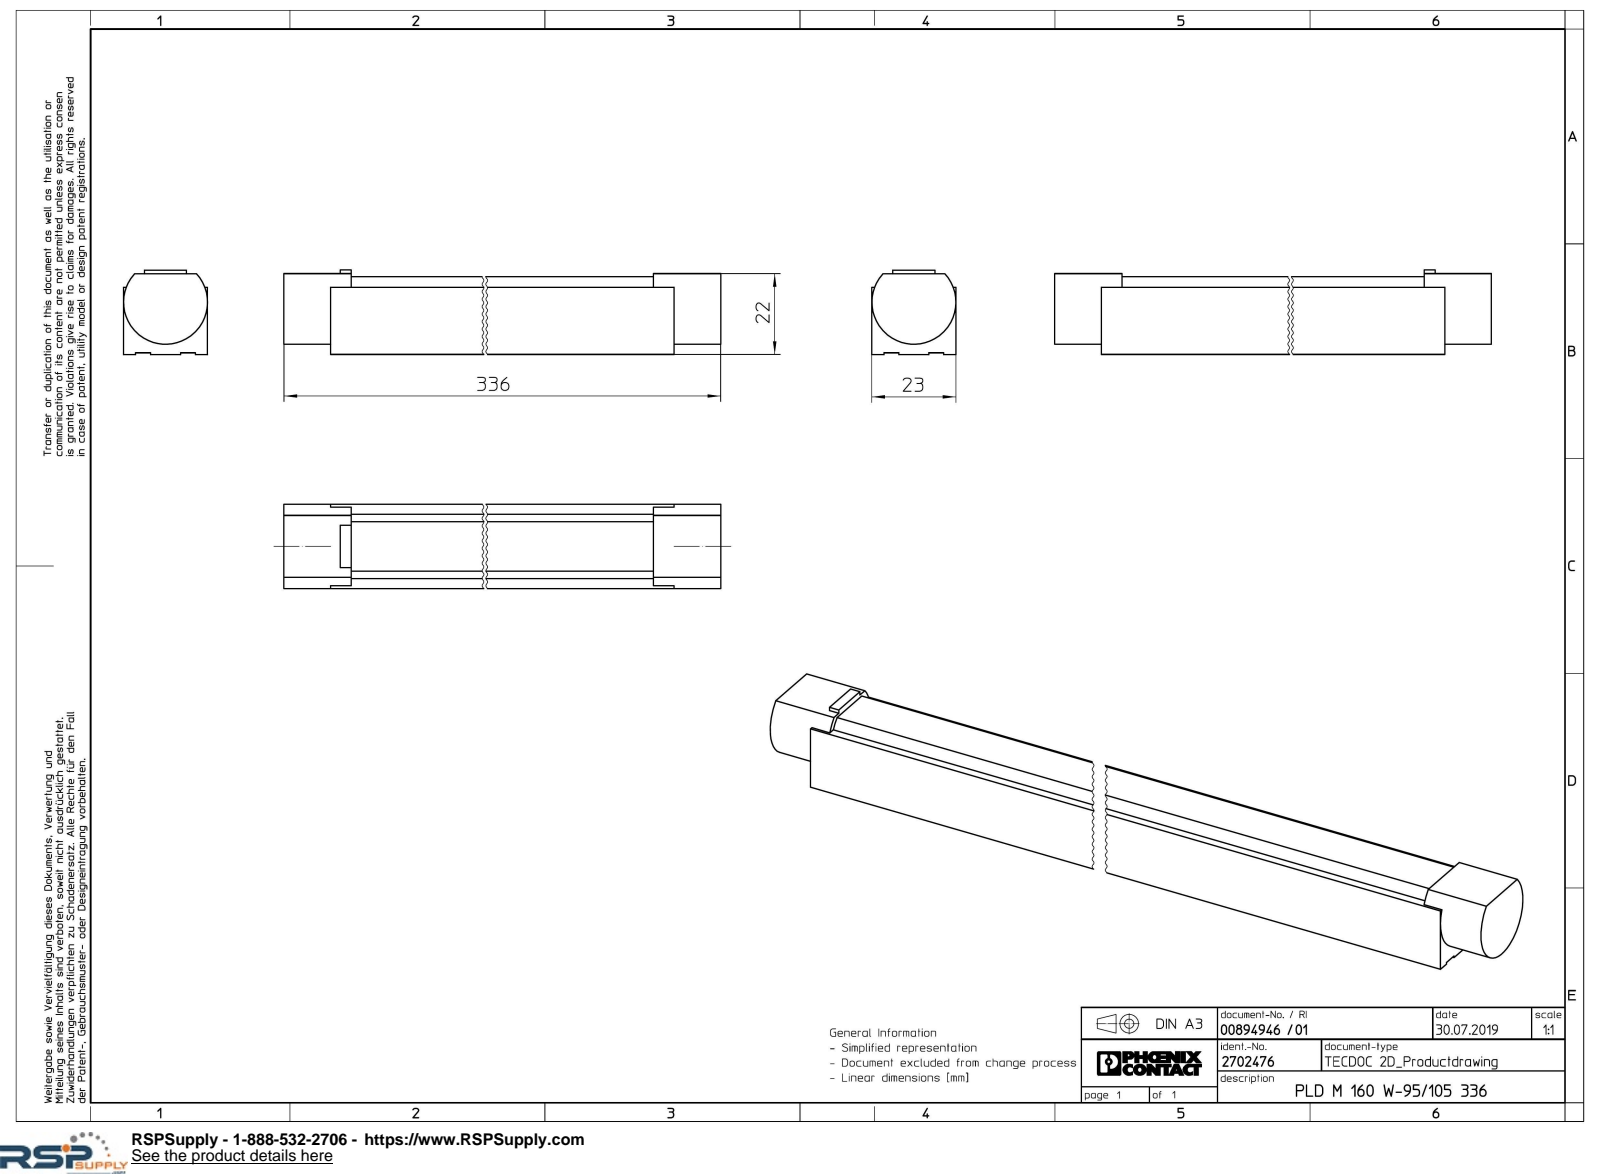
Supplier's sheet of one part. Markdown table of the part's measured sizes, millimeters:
| quantity | value |
| --- | --- |
| part name | PLD_M_160_W_95_105_336-select |
| STEP written by | Creo Elements/Direct Modeling 20.1A 29-Sep-2018 (C) Parametric Technology GmbH (AUTOMOTIVE_DESIGN) |
| units | millimeters |
| bodies | 1 solid, 40 faces (32 planar, 8 cylindrical, 0 other) |
| overall size | 336 × 22.6 × 22.5 |
| volume | 147 327 mm³ |
| surface area | 29 556 mm² |
| round holes (diameter × count) | 4.4 × 2 |
| partial cylindrical surfaces (radius × count) | 9.5 × 1, 11.25 × 1 |
| main face-to-face distances | 22.5, 20.8, 0.5, 20.3, 18, 17.5, 2.8, 21.6, 21.1, 3.6 |
| hole center spacings | 290 |
